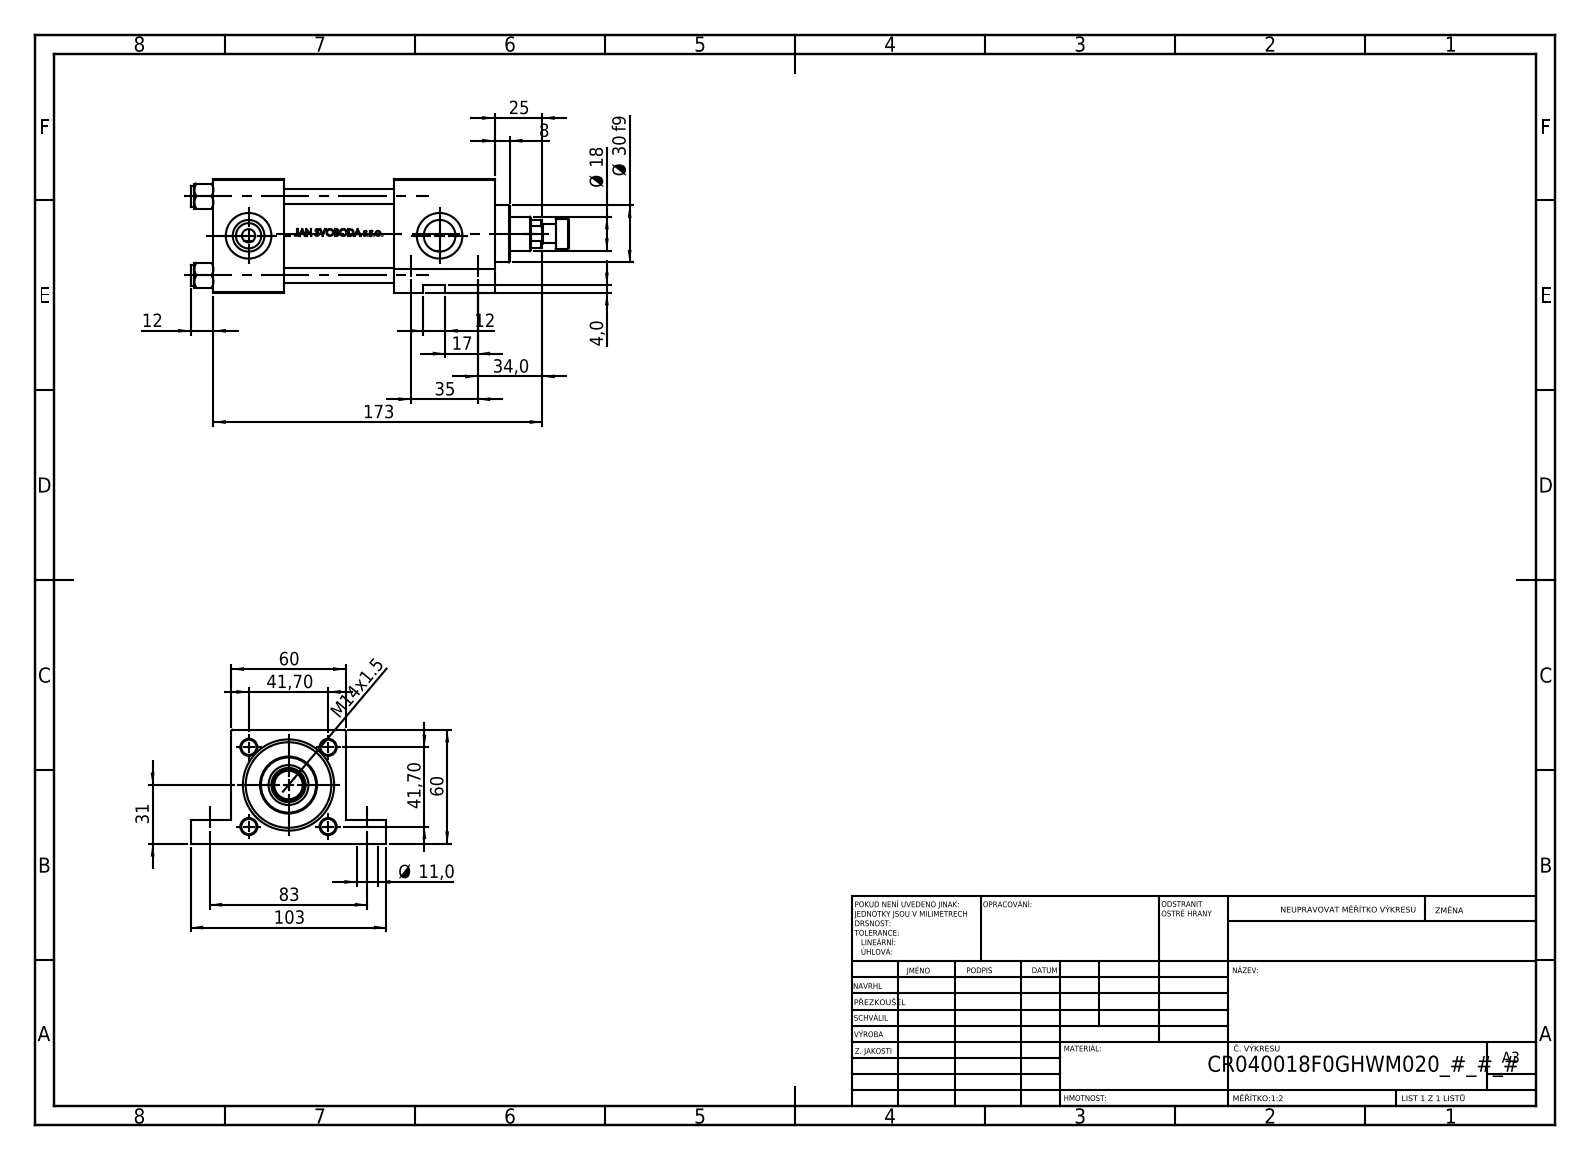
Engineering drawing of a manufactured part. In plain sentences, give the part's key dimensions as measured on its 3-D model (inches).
The part is named "V215CR_F_Body; V215_VC_A; V215CR_ROD_END_W; V215CR_VCP_F (+2 more)". Its 3-D file was written by "SolidWorks 2019 (CONFIG_CONTROL_DESIGN)". It is 12 solids with 1131 faces: 440 planar, 145 cylindrical and 546 other. Overall it measures 7.835 by 4.055 by 2.362 inches. Its volume is 25.97 cubic inches and its surface area 174.4 square inches. Round holes: 4 of diameter 0.315, 2 of diameter 0.276, 2 of diameter 0.433, 2 of diameter 0.433, 2 of diameter 0.656, 2 of diameter 0.945, 1 of diameter 0.335, 1 of diameter 0.709, 1 of diameter 0.827, 1 of diameter 1.22, 1 of diameter 1.575, 1 of diameter 1.772. Round bosses or shafts: 4 of diameter 0.433, 1 of diameter 1.811, 1 of diameter 1.181, 1 of diameter 0.63, 1 of diameter 0.394. Partial cylindrical surfaces (rounded edges, fillets, slot ends): 1 of radius 0.335. The main face-to-face distances are 2.362, 1.457, 5.827, 4.37, 2.283, 3.74, 2.087, 4.697, 3.24, 0.957. The hole center spacings are 1.642, 1.133, 1.189, 1.378, 2.322, 3.268, 3.546, 3.957.
